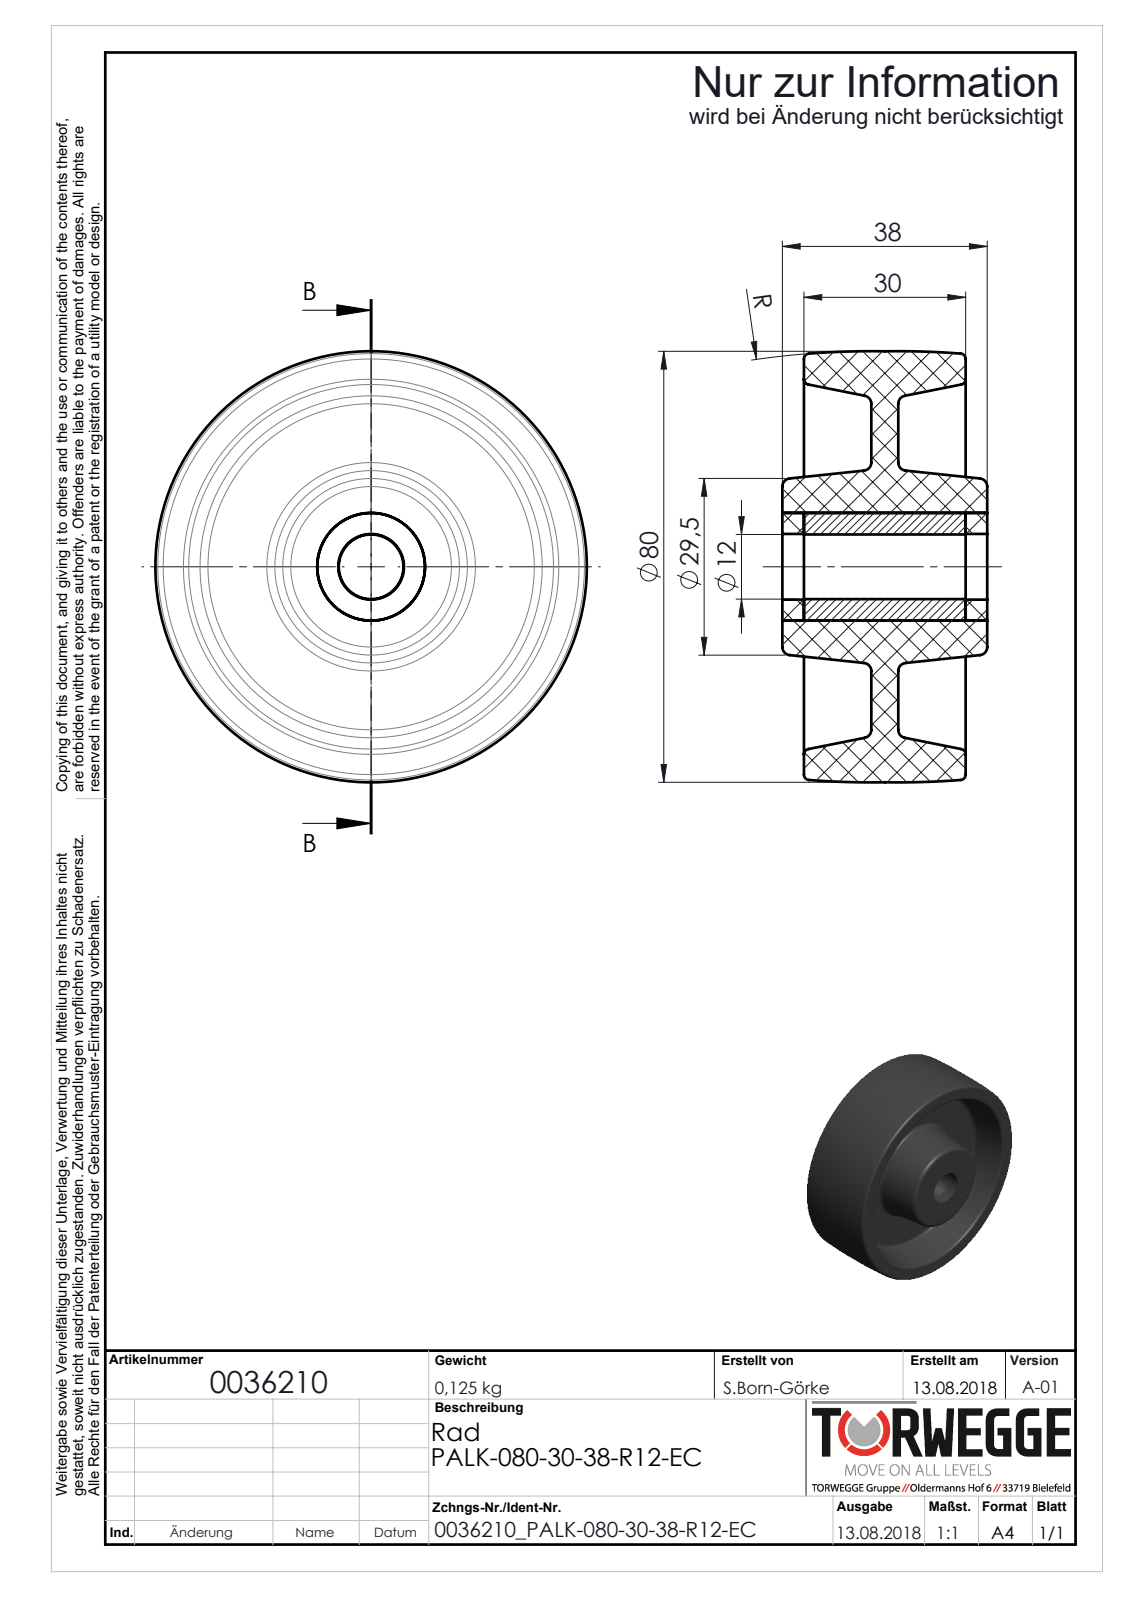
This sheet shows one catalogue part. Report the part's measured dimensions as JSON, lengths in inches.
{"part_name": "0036210_PALK-080-30-38-R12-EC", "step_written_by": "SolidWorks 2018 (AUTOMOTIVE_DESIGN)", "units": "inches", "bodies": {"solids": 4, "faces": 58, "planar": 12, "cylindrical": 14, "other": 32}, "overall_size": [3.151, 3.151, 1.496], "volume_in3": 5.594, "surface_area_in2": 47.82, "round_holes": [[0.472, 1], [0.48, 1]], "round_bosses_or_shafts": [[0.787, 1]], "face_to_face_distances": [0.492, 0.689, 0.197, 1.181, 0.157, 0.65, 0.846, 1.339, 1.496]}
